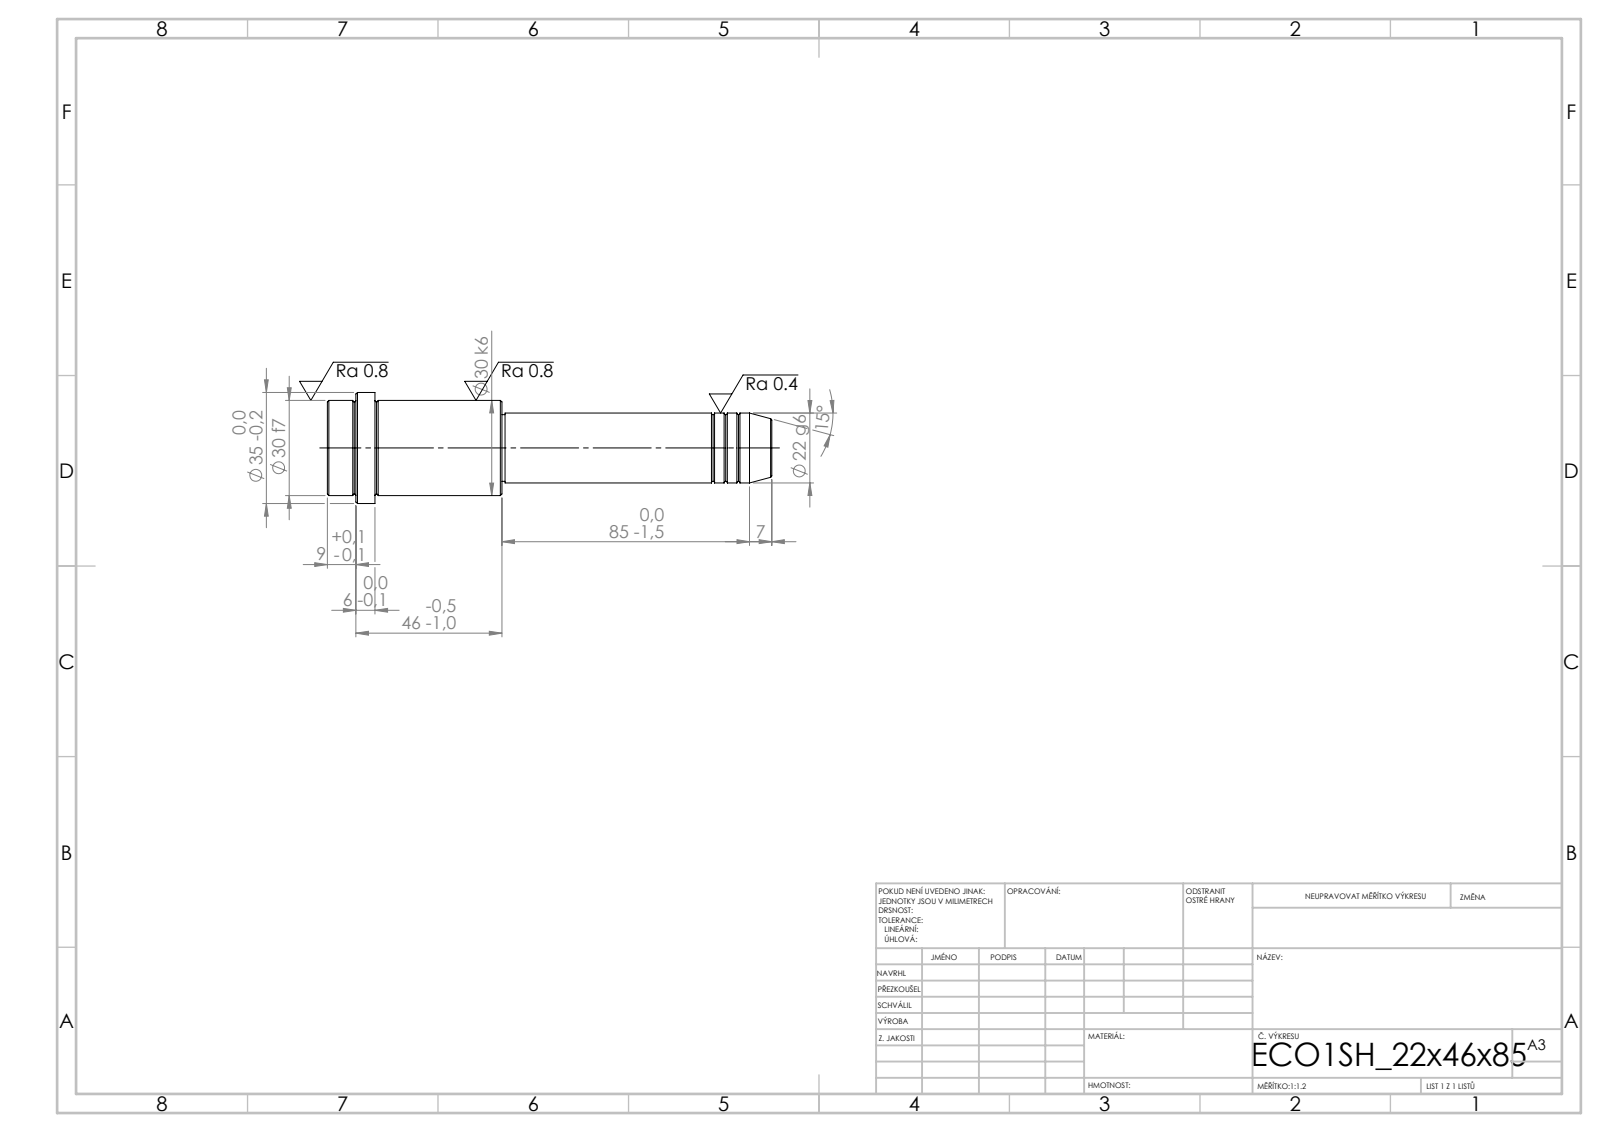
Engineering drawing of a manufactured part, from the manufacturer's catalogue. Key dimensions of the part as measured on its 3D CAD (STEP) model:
STEP written by: SolidWorks 2019 (CONFIG_CONTROL_DESIGN)
Units: millimetres
Bodies: 1 solid, 52 faces (6 planar, 16 cylindrical, 30 other)
Overall size (bounding box): 140 × 35 × 35
Volume: 72 067 mm³ · Surface area: 13 112 mm²
Round bosses / shafts (diameter × count): ⌀35 ×1, ⌀30 ×1, ⌀22 ×1, ⌀21 ×1
Main face-to-face distances: 55, 40, 15, 85, 125, 140, 131, 46, 6, 9
